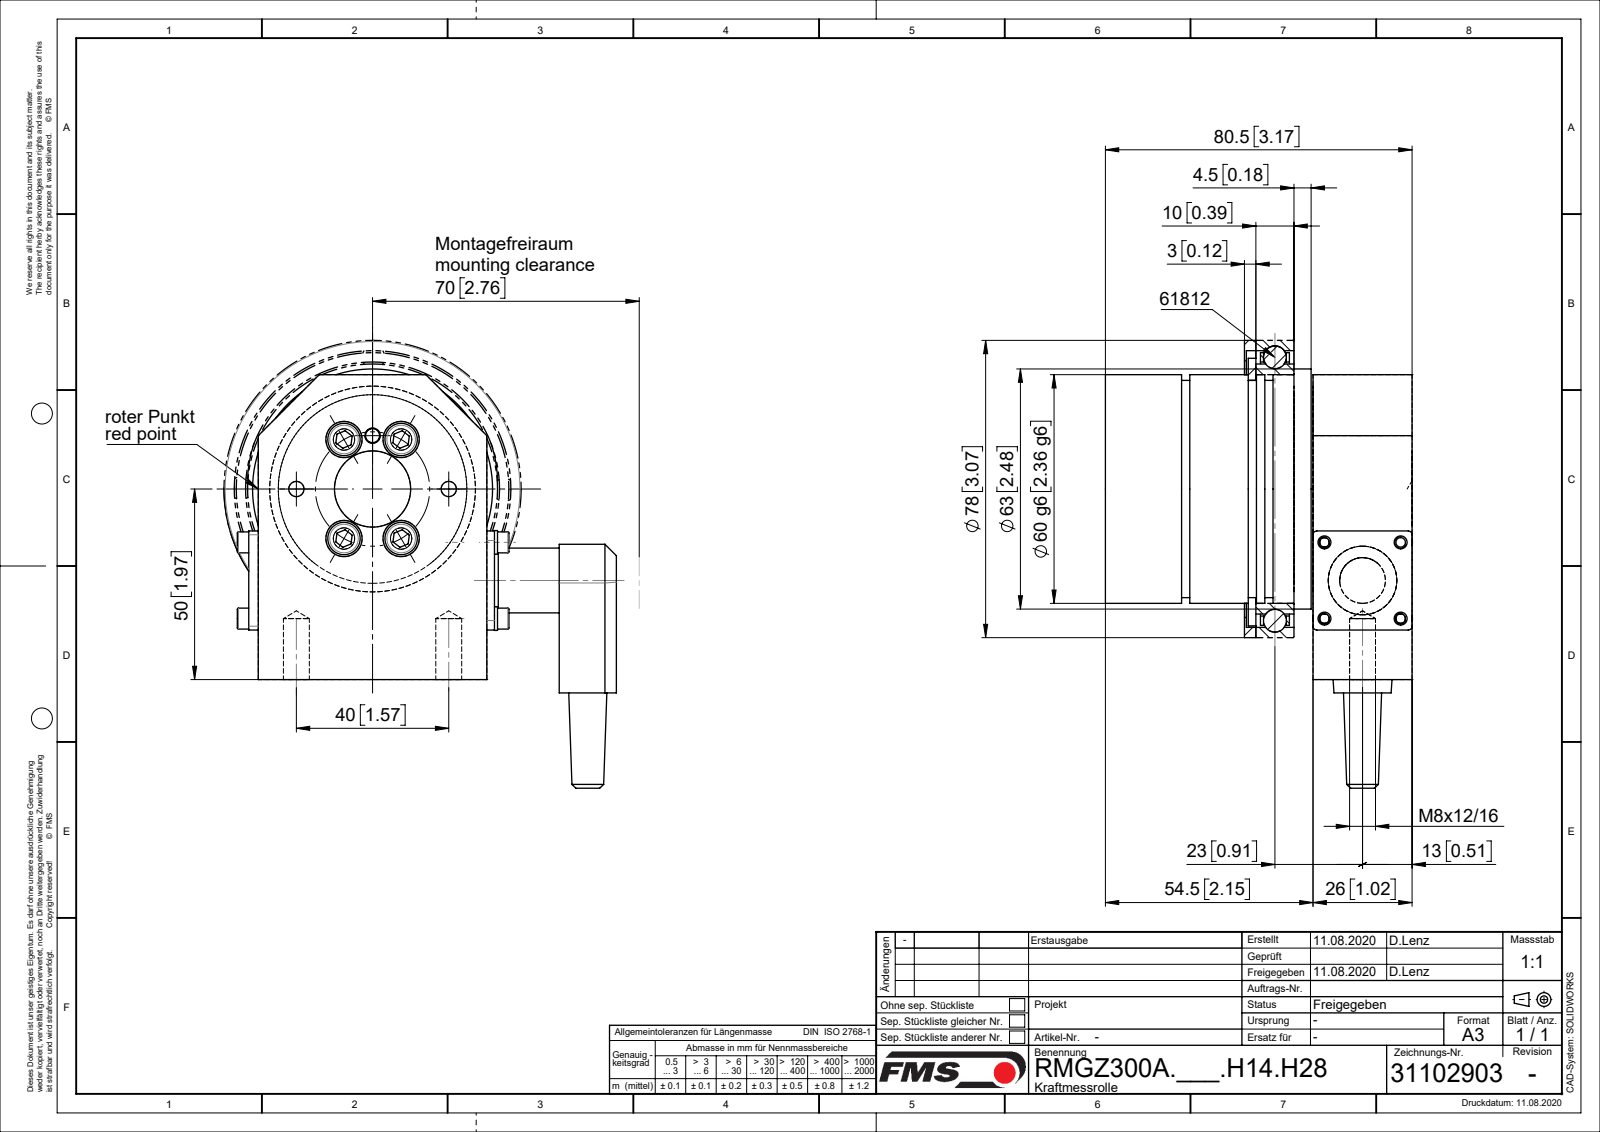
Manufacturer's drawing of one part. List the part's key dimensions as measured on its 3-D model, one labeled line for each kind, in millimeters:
Part name (STEP PRODUCT): R1307181; R51047; R1110253; I-6KT_SCHRAUBE_M5X8 (+8 more)
STEP written by: Mechanical Desktop 2009 (CONFIG_CONTROL_DESIGN)
Units: millimetres
Bodies: 27 solids, 546 faces (150 planar, 267 cylindrical, 129 other)
Overall size (bounding box): 122 × 103.5 × 90.5
Volume: 260 321 mm³ · Surface area: 98 868 mm²
Round holes (diameter × count): ⌀2 ×5, ⌀4 ×5, ⌀2.6 ×4, ⌀3.2 ×4, ⌀3.4 ×4, ⌀5.6 ×4, ⌀9 ×4, ⌀9.5 ×4, ⌀7.15 ×2, ⌀5 ×1, ⌀12 ×1, ⌀15 ×1
Round bosses / shafts (diameter × count): ⌀1.5 ×5, ⌀8 ×4, ⌀5.5 ×4, ⌀5 ×4, ⌀3 ×4, ⌀81 ×1, ⌀78 ×1, ⌀68.6 ×1
Partial cylindrical surfaces — rounded edges, fillets, slot ends (radius × count): R1 ×4, R2.5 ×4, R9.5 ×1
Main face-to-face distances: 35, 12.5, 3, 32, 44, 17, 2.5, 47.5, 37.5, 15
Hole centre spacings: 15, 14.14, 20, 3, 3.14, 3.65, 3.96, 6
